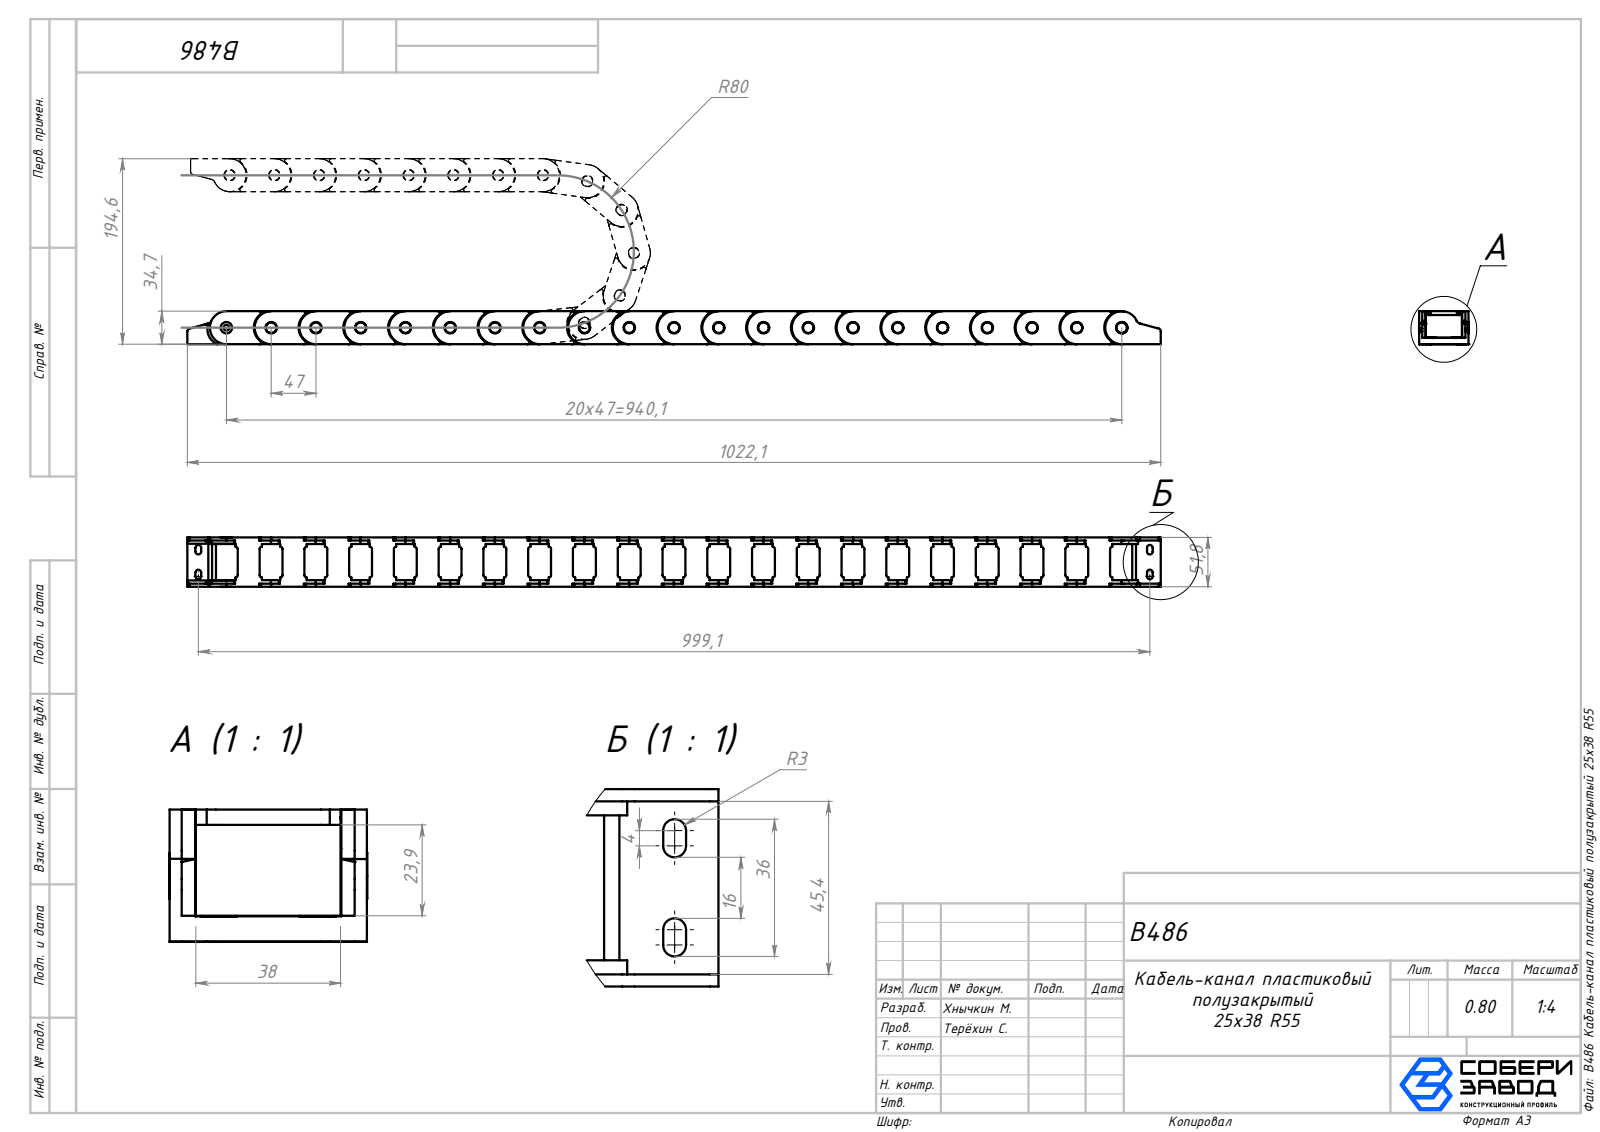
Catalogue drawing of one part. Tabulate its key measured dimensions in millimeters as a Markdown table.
| quantity | value |
| --- | --- |
| part name | Сред звено_00; нач звено_00; Конеч звено_00; B486 Кабель-канал пластиковый полузакрытый 25x38 R55 |
| STEP written by | SolidWorks 2025 (AUTOMOTIVE_DESIGN) |
| units | millimeters |
| bodies | 22 solids, 1655 faces (739 planar, 836 cylindrical, 80 other) |
| overall size | 1022.1 × 52 × 34.7 |
| volume | 616 880 mm³ |
| surface area | 349 837 mm² |
| round holes (diameter × count) | 12 × 21, 6 × 1 |
| round bosses / shafts (diameter × count) | 12 × 20 |
| partial cylindrical surfaces (radius × count) | 17.35 × 82, 2.4 × 80, 1 × 40, 2 × 40, 3 × 10, 5 × 2, 17.3 × 2 |
| main face-to-face distances | 3.2, 48.6, 6.9, 44.9, 3.7, 41.7, 45.4, 4, 30.7, 51.8 |
| hole center spacings | 47, 94, 141, 188, 235, 282, 329, 376 |
